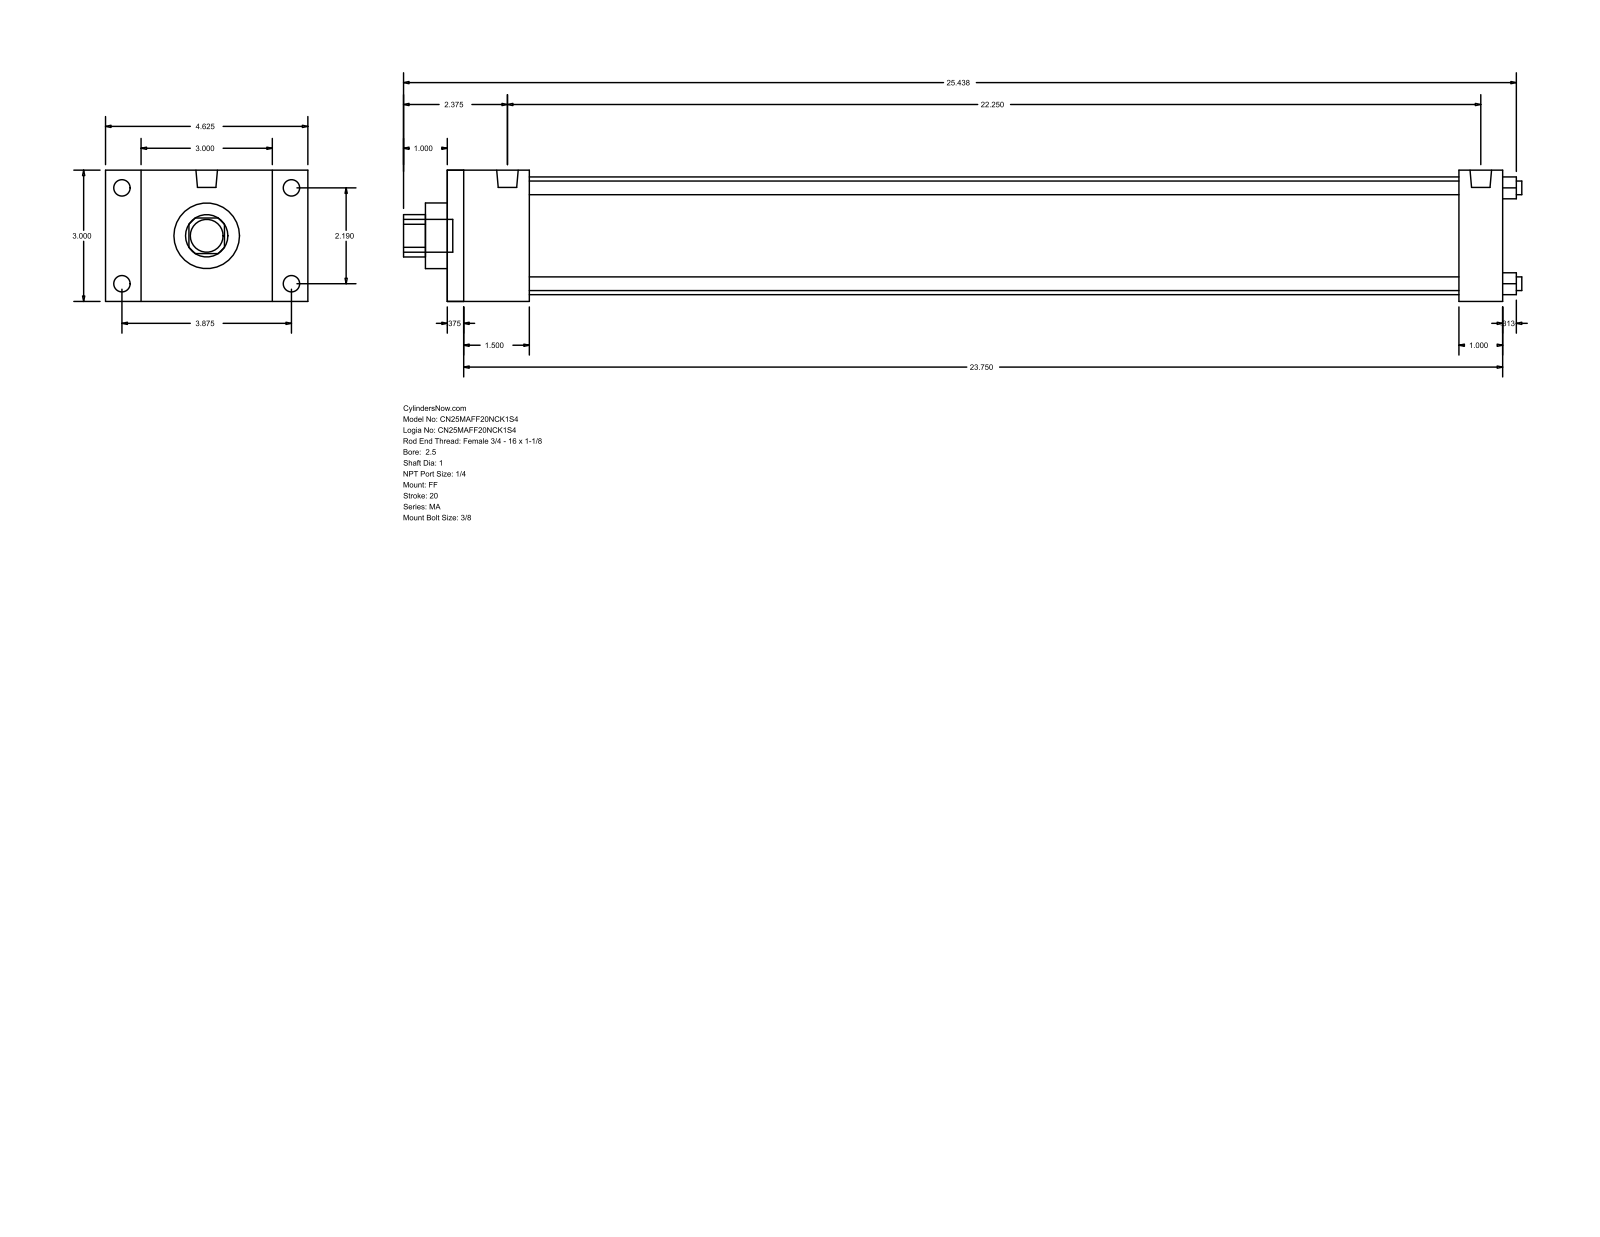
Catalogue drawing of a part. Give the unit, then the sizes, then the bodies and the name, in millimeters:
Units: millimetres
Overall size (bounding box): 649.29 × 117.47 × 76.2
Round holes (diameter × count): ⌀7.94 ×4, ⌀25.4 ×1, ⌀38.1 ×1, ⌀68.33 ×1
Round bosses / shafts (diameter × count): ⌀9.53 ×4, ⌀7.94 ×4, ⌀12.49 ×2, ⌀19.05 ×1
Partial cylindrical surfaces — rounded edges, fillets, slot ends (radius × count): R12.29 ×1
Main face-to-face distances: 76.2, 612.77, 9.52, 603.25, 25.4, 47.63, 587.37, 38.11, 577.85, 539.74
Hole centre spacings: 39.33, 55.62, 78.66
Bodies: 0 solids, 92 faces (64 planar, 28 cylindrical, 0 other)
Part name (STEP PRODUCT): MA_FF__0250_1
STEP written by: GSSL Pune (CONFIG_CONTROL_DESIGN)
